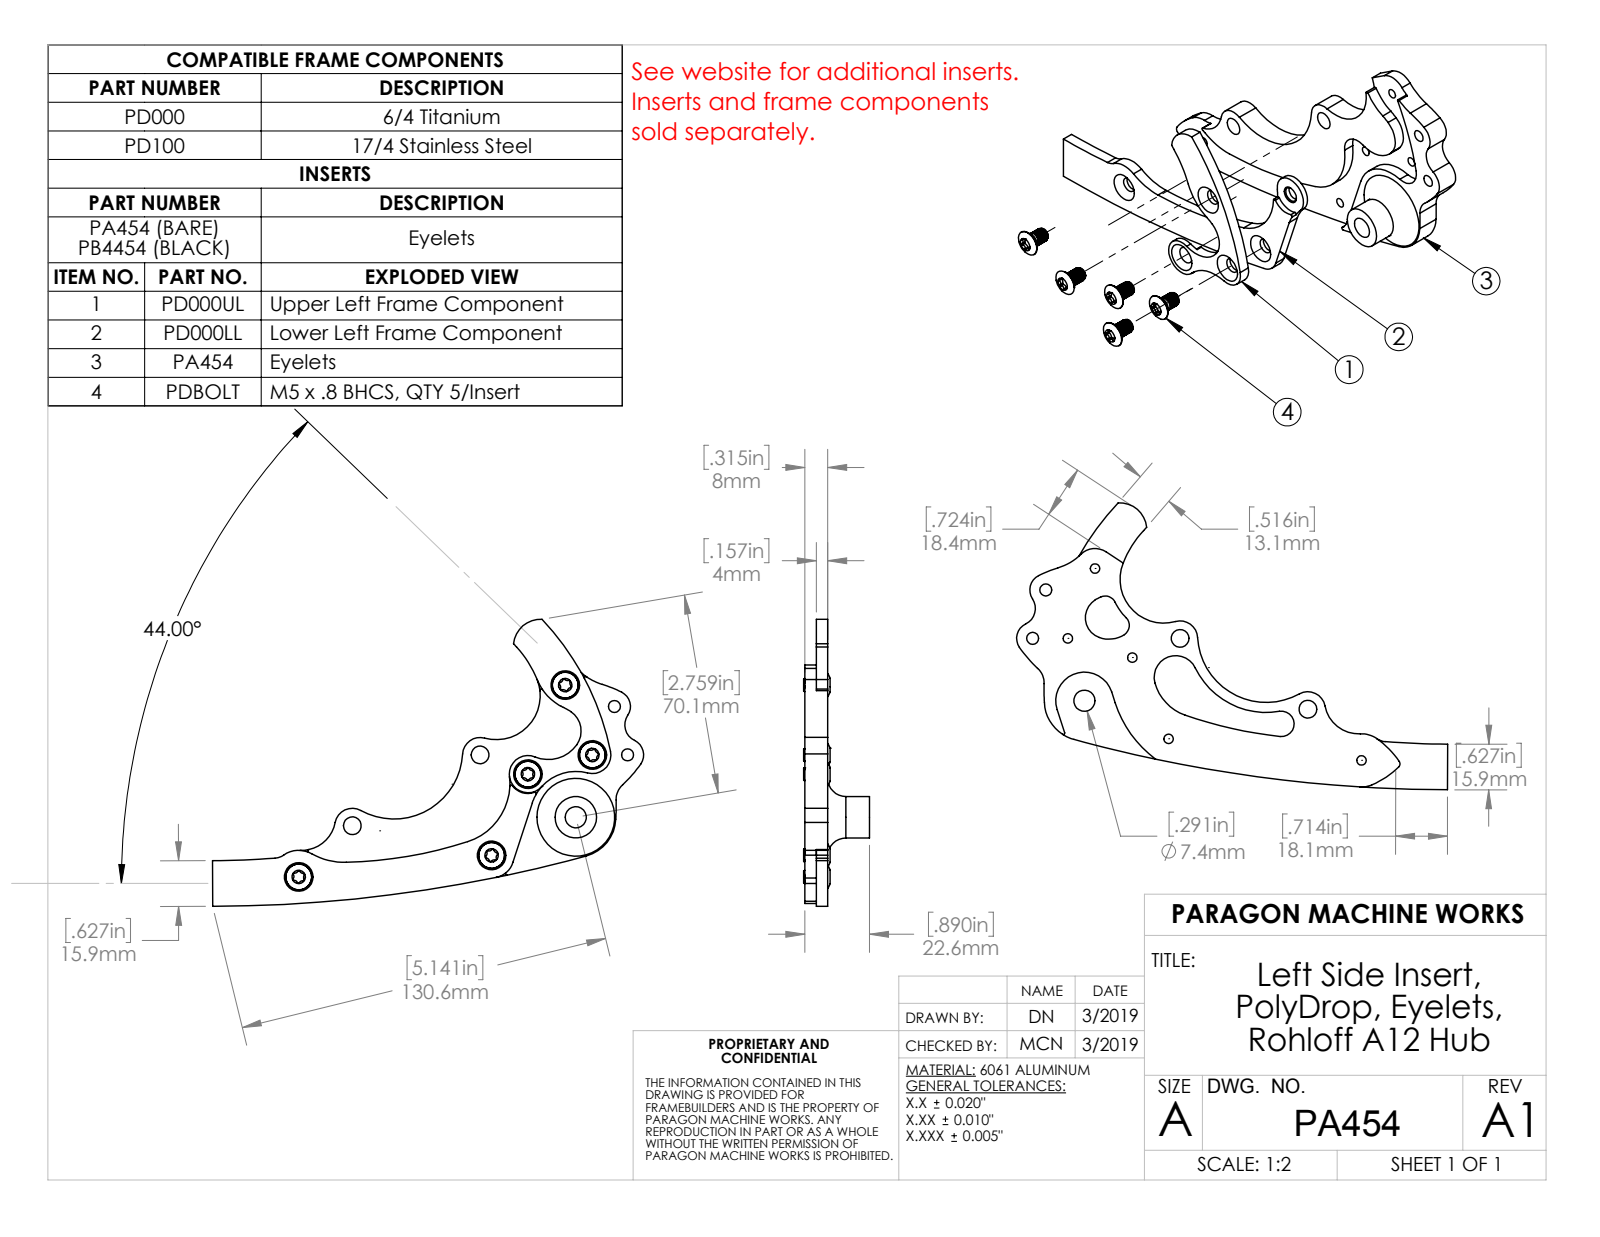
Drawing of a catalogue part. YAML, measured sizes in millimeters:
part_name: "PA454"
step_written_by: "SolidWorks 2019 (AUTOMOTIVE_DESIGN)"
units: millimeters
bodies: {solids: 1, faces: 100, planar: 12, cylindrical: 86, other: 2}
overall_size: [133.88, 83.25, 22.6]
volume: 26422
surface_area: 15710
round_holes:
  - {diameter: 3.3, count: 5}
  - {diameter: 4.2, count: 2}
  - {diameter: 6.2, count: 2}
  - {diameter: 7.4, count: 1}
round_bosses_or_shafts:
  - {diameter: 14.48, count: 1}
partial_cylinders:
  - {radius: 0.5, count: 5}
  - {radius: 3.81, count: 2}
  - {radius: 5.59, count: 2}
  - {radius: 6.09, count: 2}
  - {radius: 6.5, count: 2}
  - {radius: 7, count: 2}
  - {radius: 30.71, count: 2}
  - {radius: 44.03, count: 2}
face_to_face_distances: [4, 8, 2, 6, 4.5, 2.5, 0.5, 3.5, 14.6, 16.6]
hole_center_spacings: [22.5, 12.3, 17.5, 18.01, 18.6, 18.73, 23.48, 25.89]
